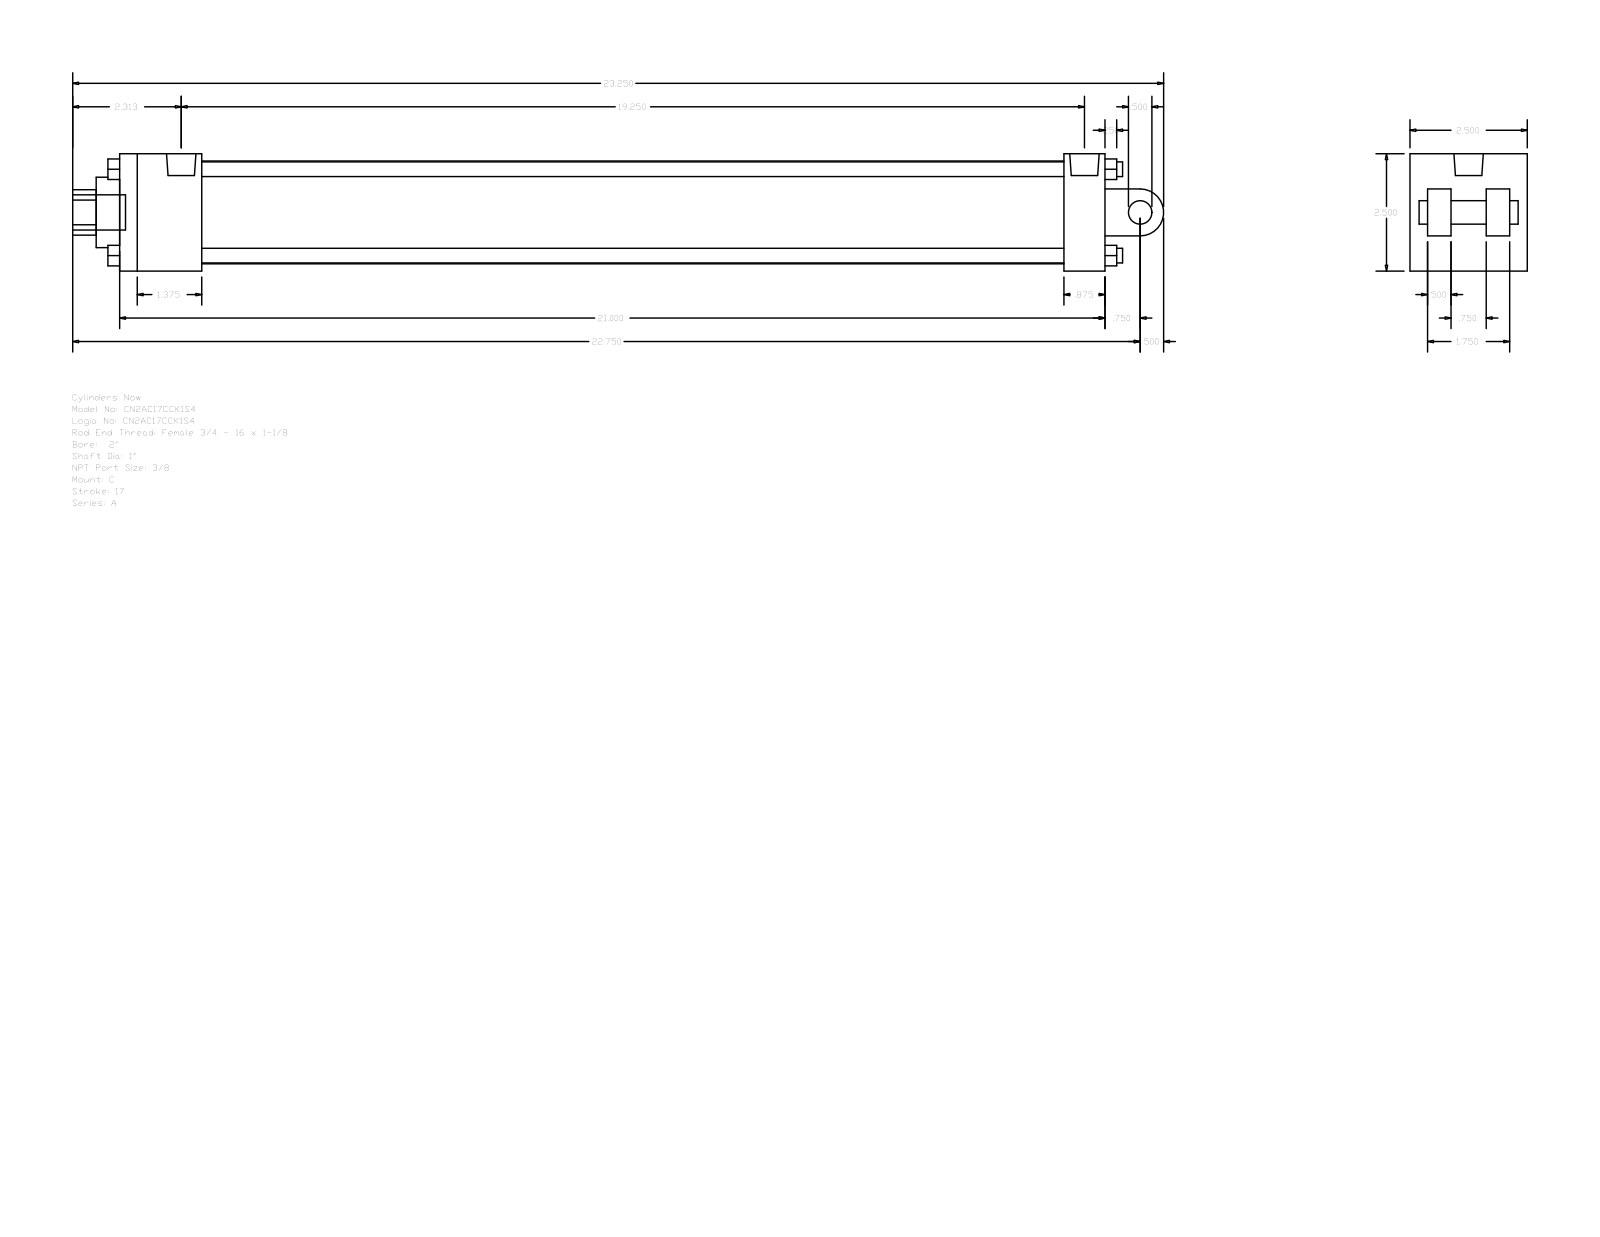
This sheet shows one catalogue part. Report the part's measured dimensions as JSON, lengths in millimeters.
{"part_name": "A_C__0200_1", "step_written_by": "GSSL Pune (CONFIG_CONTROL_DESIGN)", "units": "millimeters", "bodies": {"solids": 0, "faces": 135, "planar": 102, "cylindrical": 33, "other": 0}, "overall_size": [590.55, 63.5, 63.5], "round_holes": [[5.56, 2], [15.93, 1], [25.4, 1], [38.1, 1], [55.63, 1]], "round_bosses_or_shafts": [[7.94, 4], [5.56, 2], [19.05, 1], [15.93, 1], [12.7, 1]], "partial_cylinders_radius": [[12.29, 1], [12.7, 1]], "face_to_face_distances": [63.5, 22.22, 533.4, 44.45, 12.7, 9.52, 41.28, 488.95, 511.18, 466.73], "hole_center_spacings": [3.98]}
